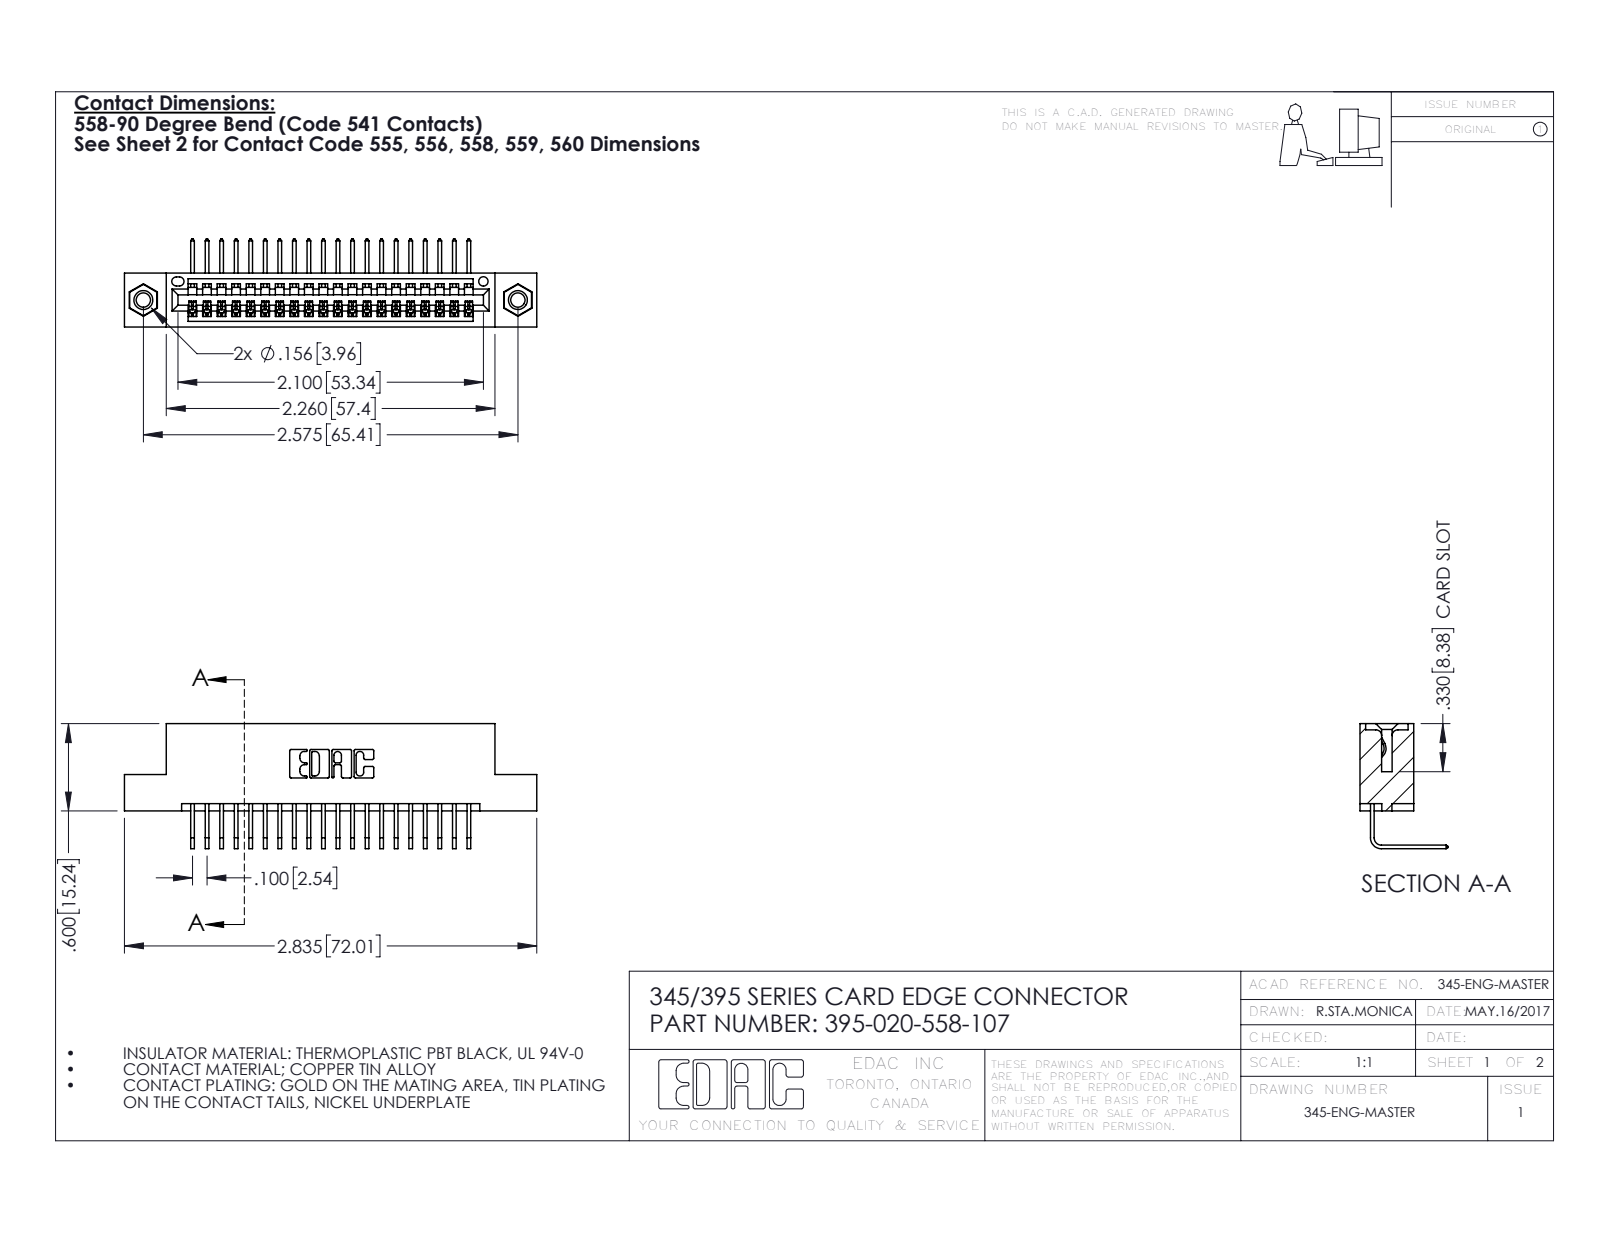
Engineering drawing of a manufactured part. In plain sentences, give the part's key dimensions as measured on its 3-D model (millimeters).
The part is named "345 Part_Flush Mounting Lugs - 0.156 Dia-TI; 395-020-558-107; 345-292-001_558 Tail - 2; 345-250-001_345-250-005-103". Its 3-D file was written by "SolidWorks 2016 (CONFIG_CONTROL_DESIGN)". It is 23 solids with 1386 faces: 952 planar, 418 cylindrical and 16 other. Overall it measures 72 by 21.8 by 15.4 millimeters. Its volume is 6 720 cubic millimeters and its surface area 9 045 square millimeters. Round holes: 2 of diameter 2.5, 2 of diameter 3.2, 2 of diameter 4, 1 of diameter 1.6. Round bosses or shafts: 2 of diameter 3.9. Partial cylindrical surfaces (rounded edges, fillets, slot ends): 40 of radius 0.2, 22 of radius 0.3, 6 of radius 0.2, 6 of radius 0.8, 3 of radius 0.7, 2 of radius 0.8, 2 of radius 1, 1 of radius 0.4. The main face-to-face distances are 1.8, 7.6, 5.1, 9.4, 2.5, 6.9, 0.6, 5.7, 3.8, 15.2. The hole center spacings are 6.9, 59.5, 65.4.
